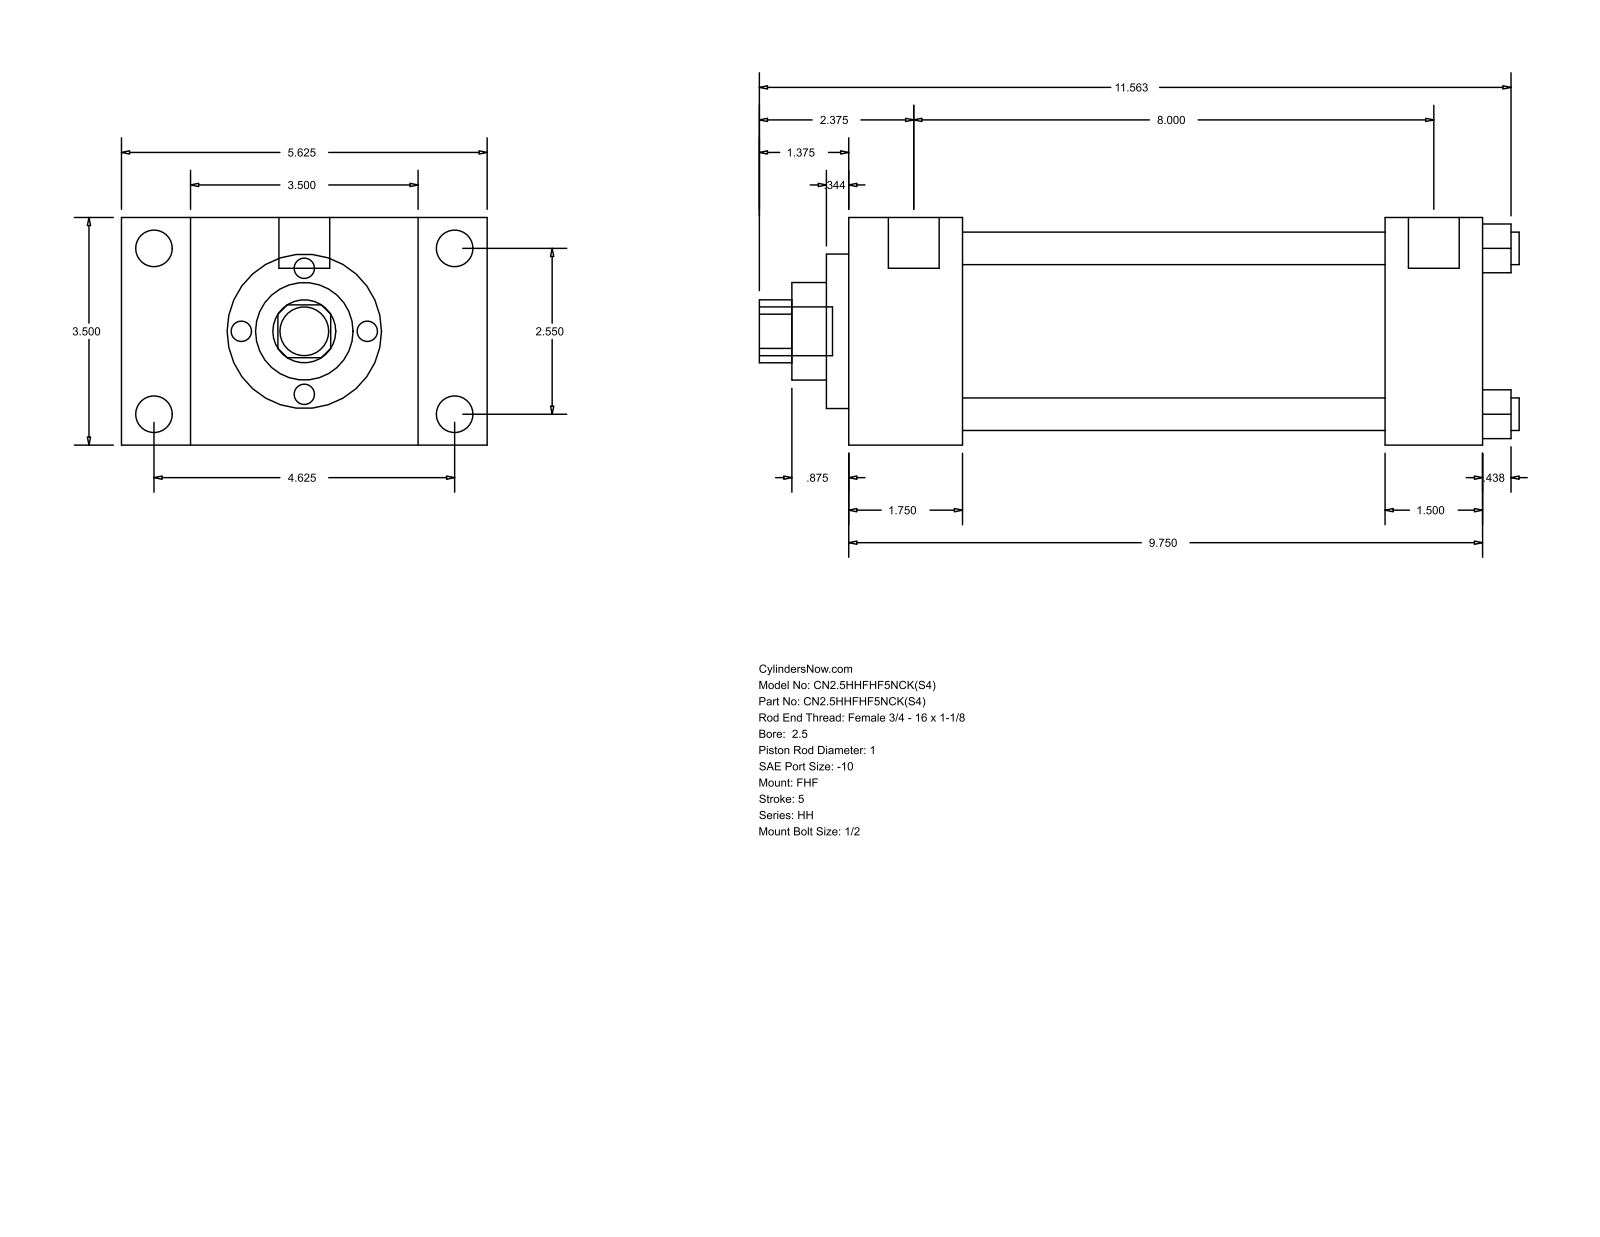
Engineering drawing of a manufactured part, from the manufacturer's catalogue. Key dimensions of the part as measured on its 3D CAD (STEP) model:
Part name (STEP PRODUCT): HH_FHF__0250_1
STEP written by: GSSL Pune (CONFIG_CONTROL_DESIGN)
Units: millimetres
Bodies: 0 solids, 90 faces (61 planar, 29 cylindrical, 0 other)
Overall size (bounding box): 296.86 × 142.88 × 88.9
Round holes (diameter × count): ⌀12.7 ×4, ⌀25.4 ×1, ⌀38.1 ×1, ⌀60.33 ×1, ⌀73.03 ×1
Round bosses / shafts (diameter × count): ⌀14.3 ×4, ⌀5.56 ×4, ⌀19.84 ×2, ⌀19.05 ×1
Partial cylindrical surfaces — rounded edges, fillets, slot ends (radius × count): R12.29 ×1
Main face-to-face distances: 88.9, 44.46, 26.99, 115.89, 247.65, 203.19, 142.88, 209.55, 165.09, 38.1
Hole centre spacings: 45.79, 64.76, 91.58
